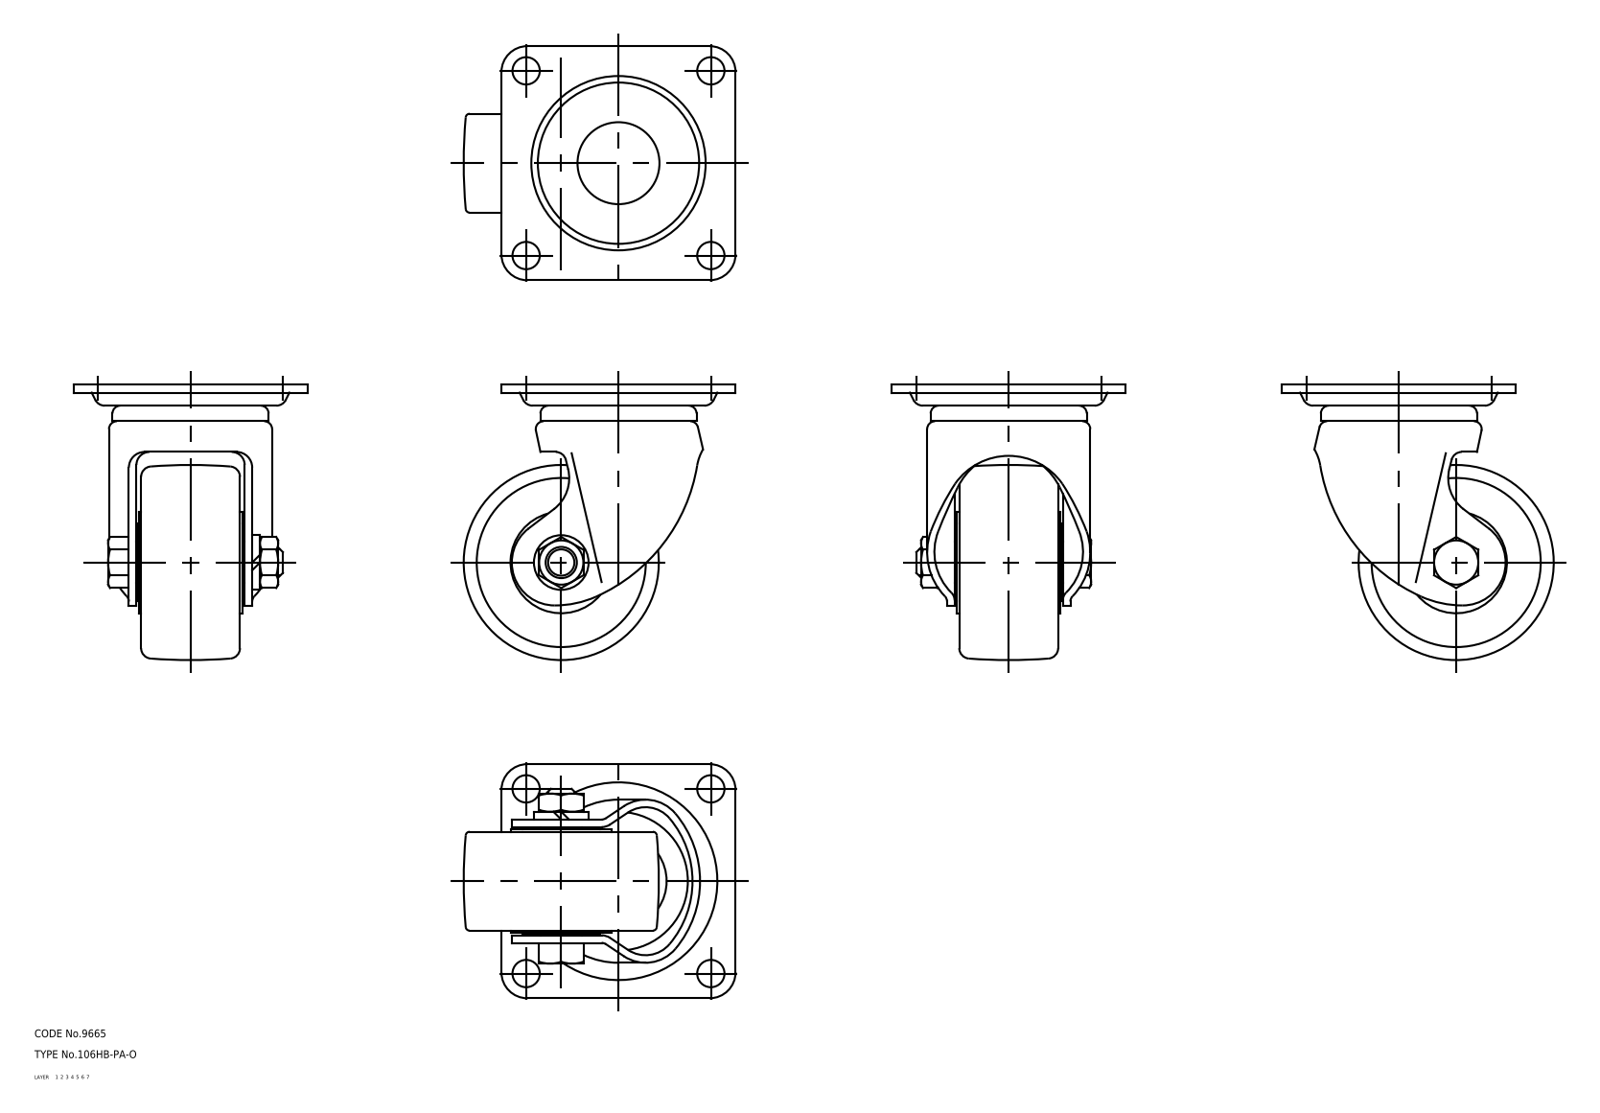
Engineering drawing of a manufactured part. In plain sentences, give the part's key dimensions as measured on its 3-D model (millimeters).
The part is named "67125557; 67125570; 67125583; 67125596 (+1 more)". Its 3-D file was written by "CADfix (AUTOMOTIVE_DESIGN)". It is 5 solids with 238 faces: 0 planar, 0 cylindrical and 238 other. Overall it measures 106 by 104.5 by 90 millimeters. Its volume is 272 681 cubic millimeters and its surface area 69 377 square millimeters.
